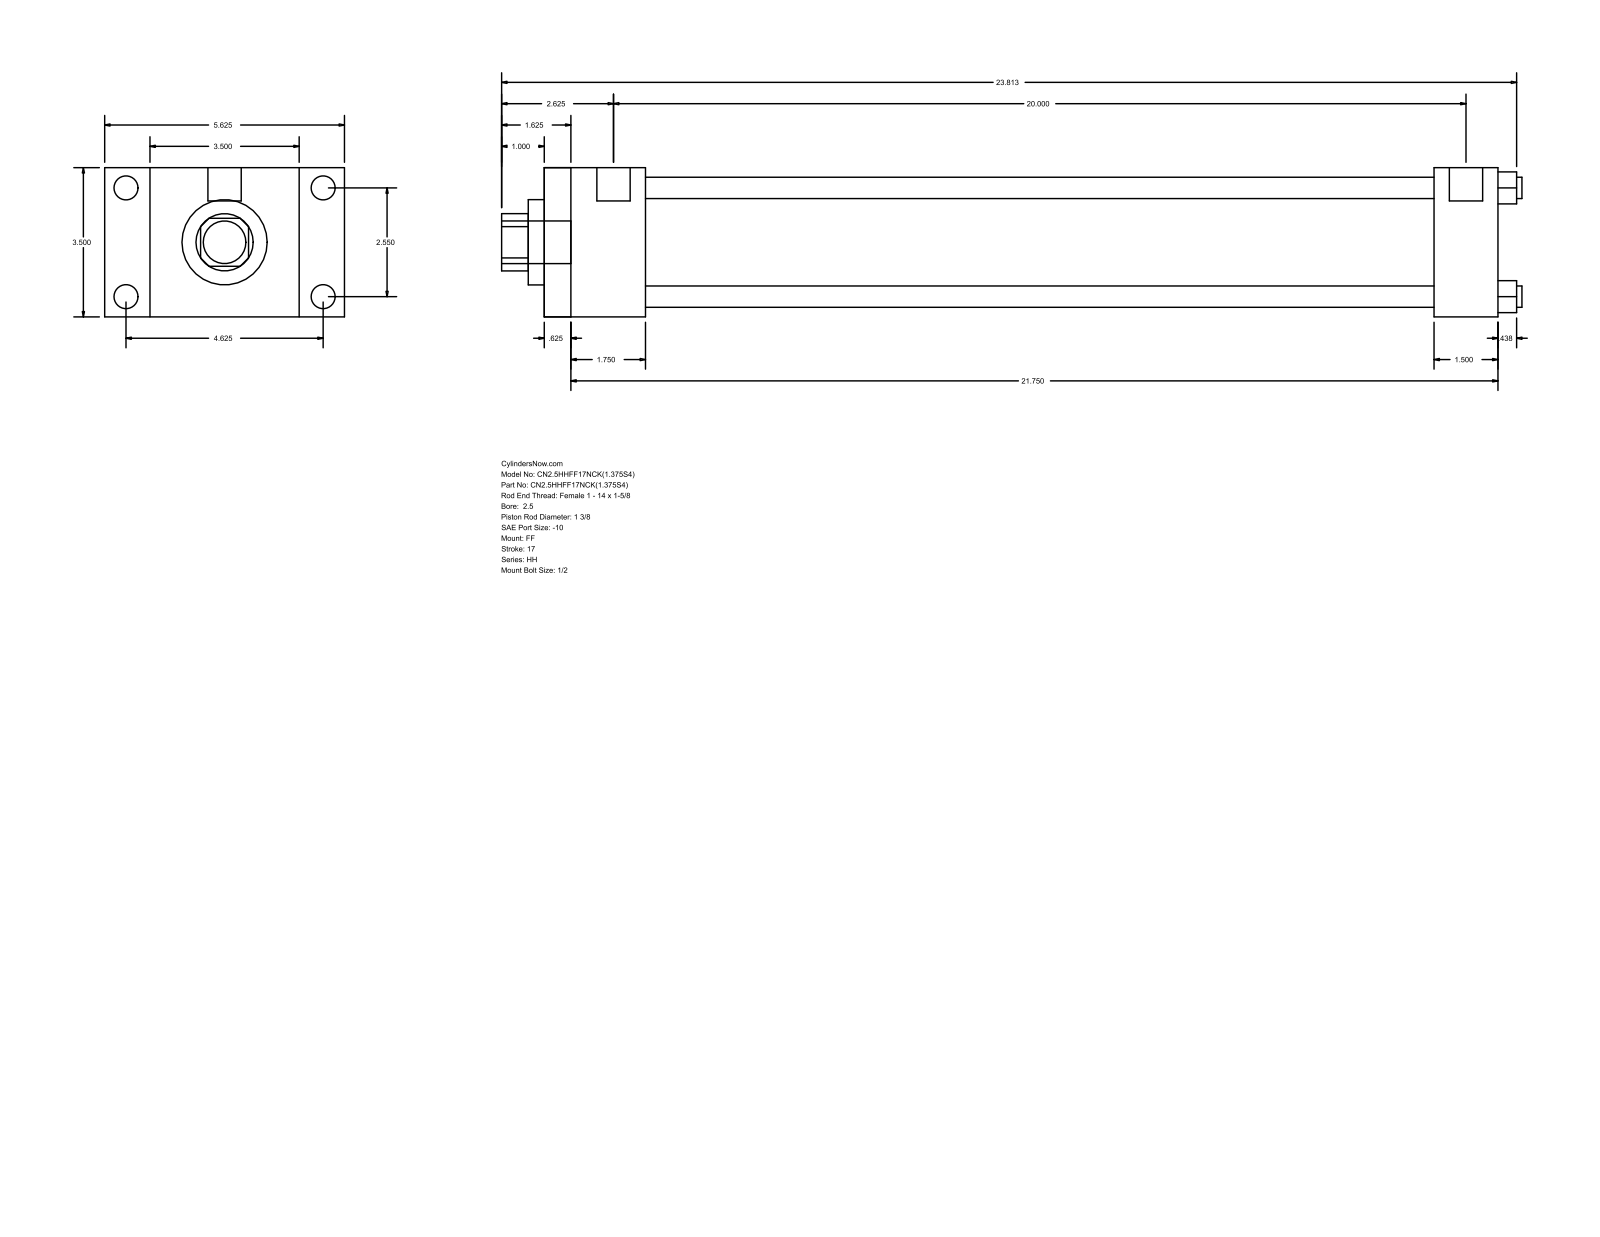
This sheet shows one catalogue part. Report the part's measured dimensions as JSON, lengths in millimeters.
{"part_name": "HH_FF__0250_1.375", "step_written_by": "GSSL Pune (CONFIG_CONTROL_DESIGN)", "units": "millimeters", "bodies": {"solids": 0, "faces": 92, "planar": 64, "cylindrical": 28, "other": 0}, "overall_size": [608.01, 142.88, 88.9], "round_holes": [[12.7, 4], [34.92, 1], [50.8, 1], [73.03, 1]], "round_bosses_or_shafts": [[14.3, 4], [5.56, 4], [19.84, 2], [25.4, 1]], "partial_cylinders_radius": [[17.06, 1]], "face_to_face_distances": [88.9, 568.33, 15.87, 552.46, 60.32, 44.45, 508.01, 530.22, 514.35, 469.9], "hole_center_spacings": [45.79, 64.76, 91.58]}
